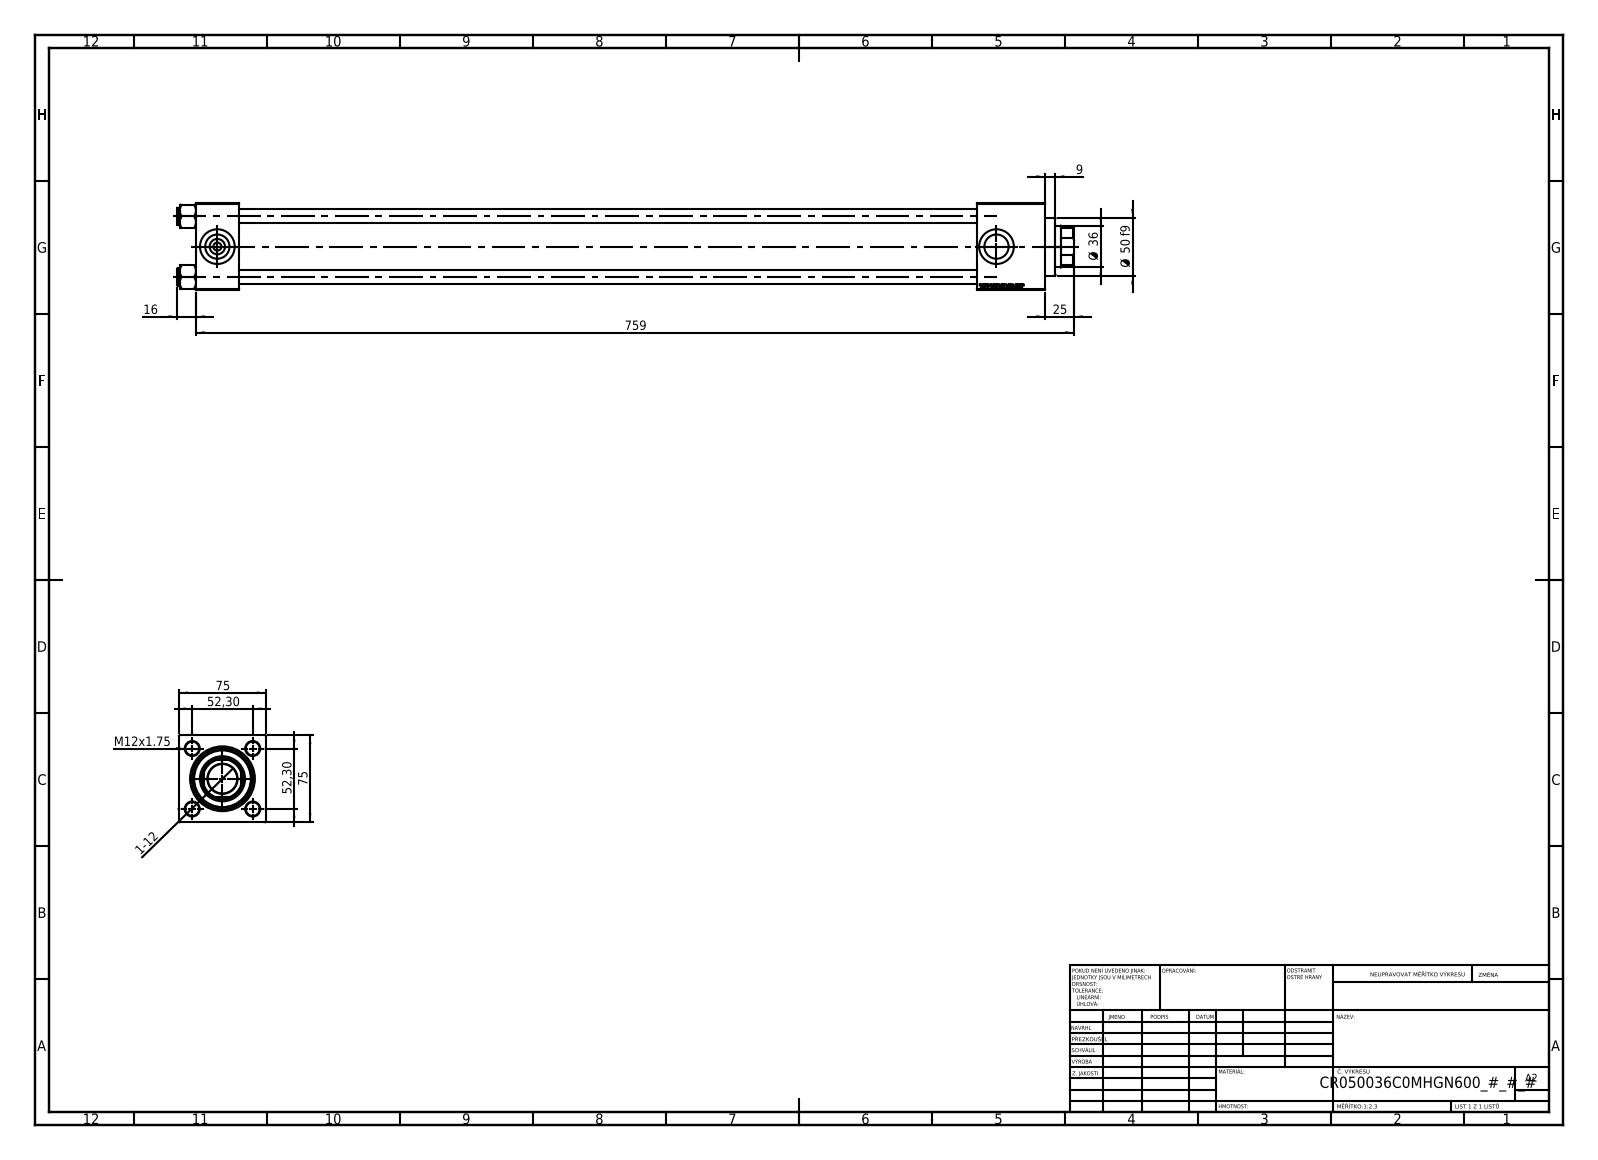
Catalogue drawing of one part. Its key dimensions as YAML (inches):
part_name: "NUT_M5_C; V215CR_C_TYCINKA; V215CR_C_Body; V215_VC_A (+1 more)"
step_written_by: "SolidWorks 2019 (CONFIG_CONTROL_DESIGN)"
units: inches
bodies: {solids: 11, faces: 1148, planar: 526, cylindrical: 86, other: 536}
overall_size: [30.512, 2.974, 2.953]
volume: 111.6
surface_area: 777.6
round_holes:
  - {diameter: 0.472, count: 4}
  - {diameter: 0.276, count: 2}
  - {diameter: 0.825, count: 2}
  - {diameter: 1.181, count: 2}
  - {diameter: 1.004, count: 1}
  - {diameter: 1.417, count: 1}
  - {diameter: 1.535, count: 1}
  - {diameter: 1.614, count: 1}
  - {diameter: 2.087, count: 1}
round_bosses_or_shafts:
  - {diameter: 0.591, count: 4}
  - {diameter: 2.205, count: 1}
  - {diameter: 1.969, count: 1}
partial_cylinders:
  - {radius: 0.689, count: 1}
face_to_face_distances: [2.953, 1.457, 26.575, 25.118, 28.898, 27.441, 2.323, 27.768, 26.311, 1.193]
hole_center_spacings: [1.456, 2.059, 2.912, 26.516]
